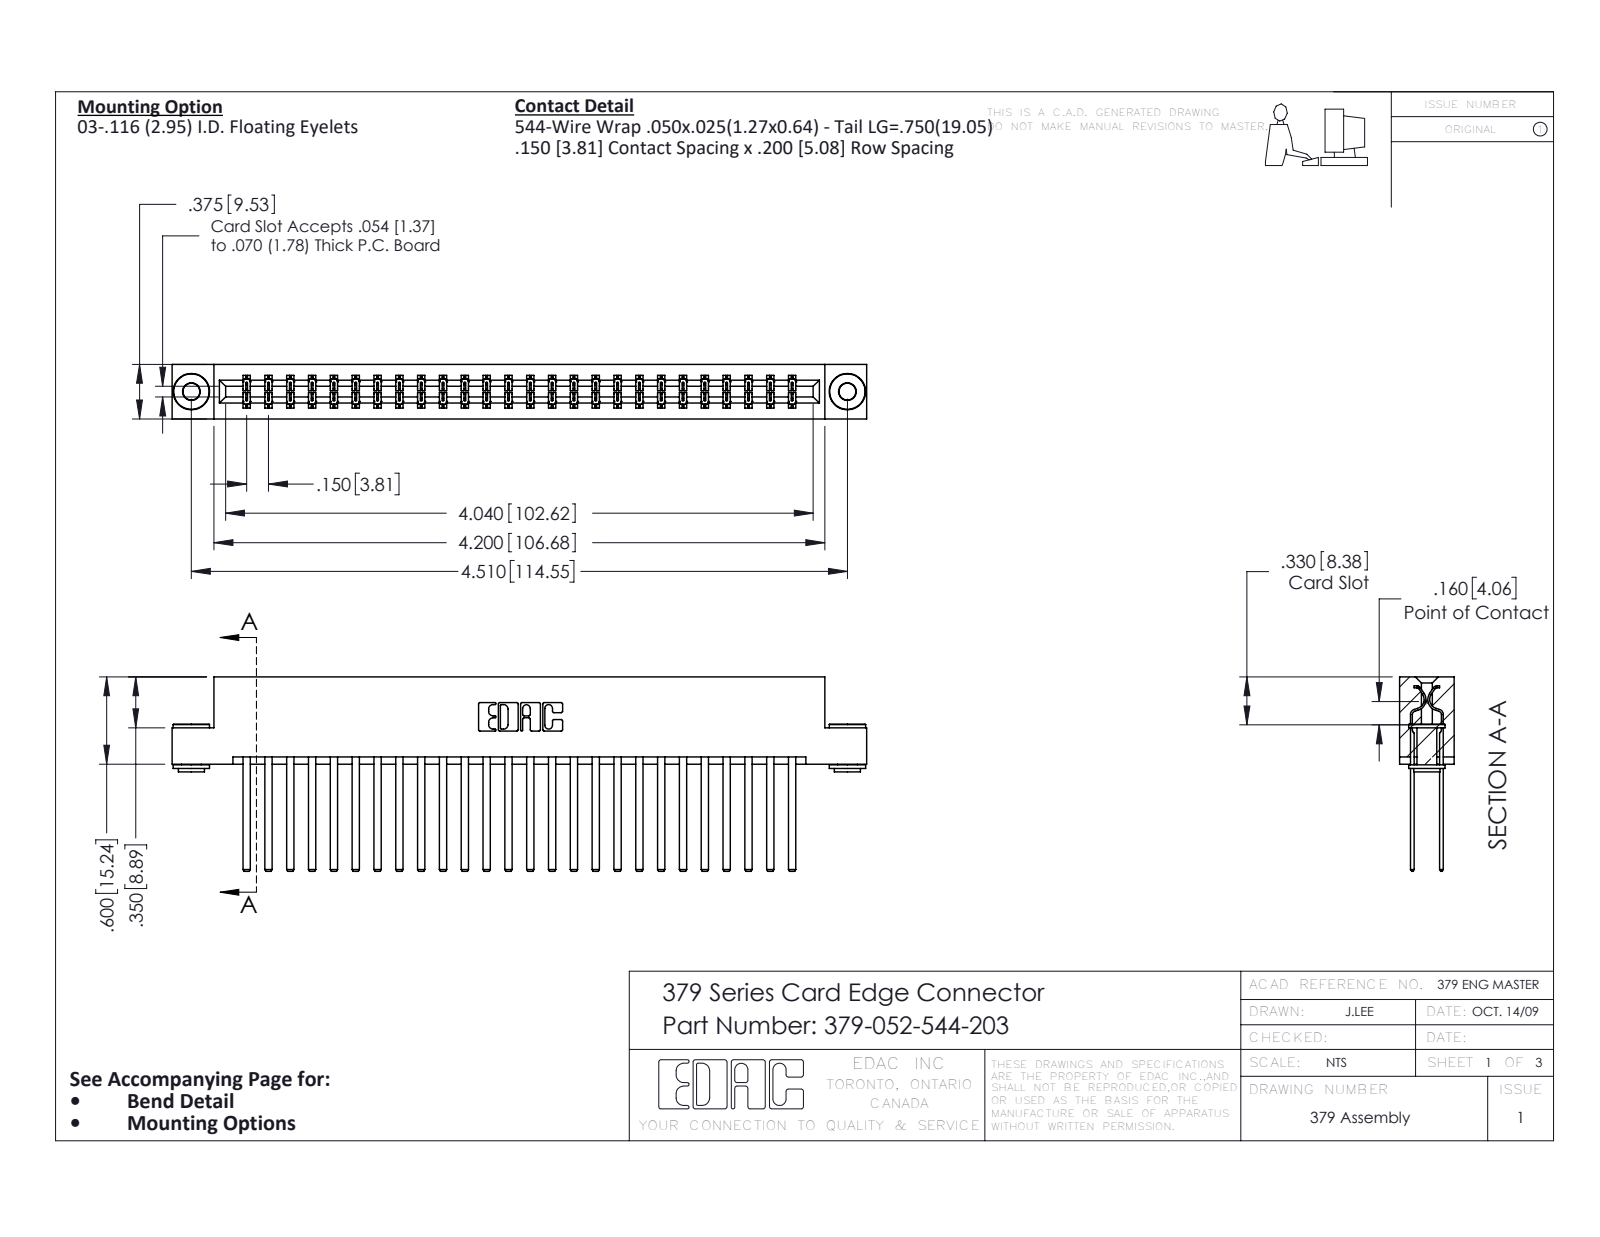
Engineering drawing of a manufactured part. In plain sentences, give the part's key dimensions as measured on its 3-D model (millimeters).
The part is named "345-250-002_345-250-002-102; 379 Part_Flush - .156 Dia - TH; 345-292-001_345-293-144; 379-052-544-203". Its 3-D file was written by "SolidWorks 2016 (CONFIG_CONTROL_DESIGN)". It is 55 solids with 2544 faces: 1744 planar, 792 cylindrical and 8 other. Overall it measures 121.3 by 34 by 9.5 millimeters. Its volume is 13 500 cubic millimeters and its surface area 17 590 square millimeters. Round holes: 2 of diameter 2.9, 2 of diameter 4. Round bosses or shafts: 2 of diameter 6.4, 2 of diameter 4.6, 2 of diameter 3.5. Partial cylindrical surfaces (rounded edges, fillets, slot ends): 78 of radius 0.2, 22 of radius 0.3, 6 of radius 0.2, 6 of radius 0.8, 3 of radius 0.7, 2 of radius 0.4, 2 of radius 0.6, 2 of radius 0.6. The main face-to-face distances are 7.6, 2.5, 1.9, 5.1, 7, 9.5, 0.6, 3.8, 15.2, 1.9. The hole center spacings are 114.6.
